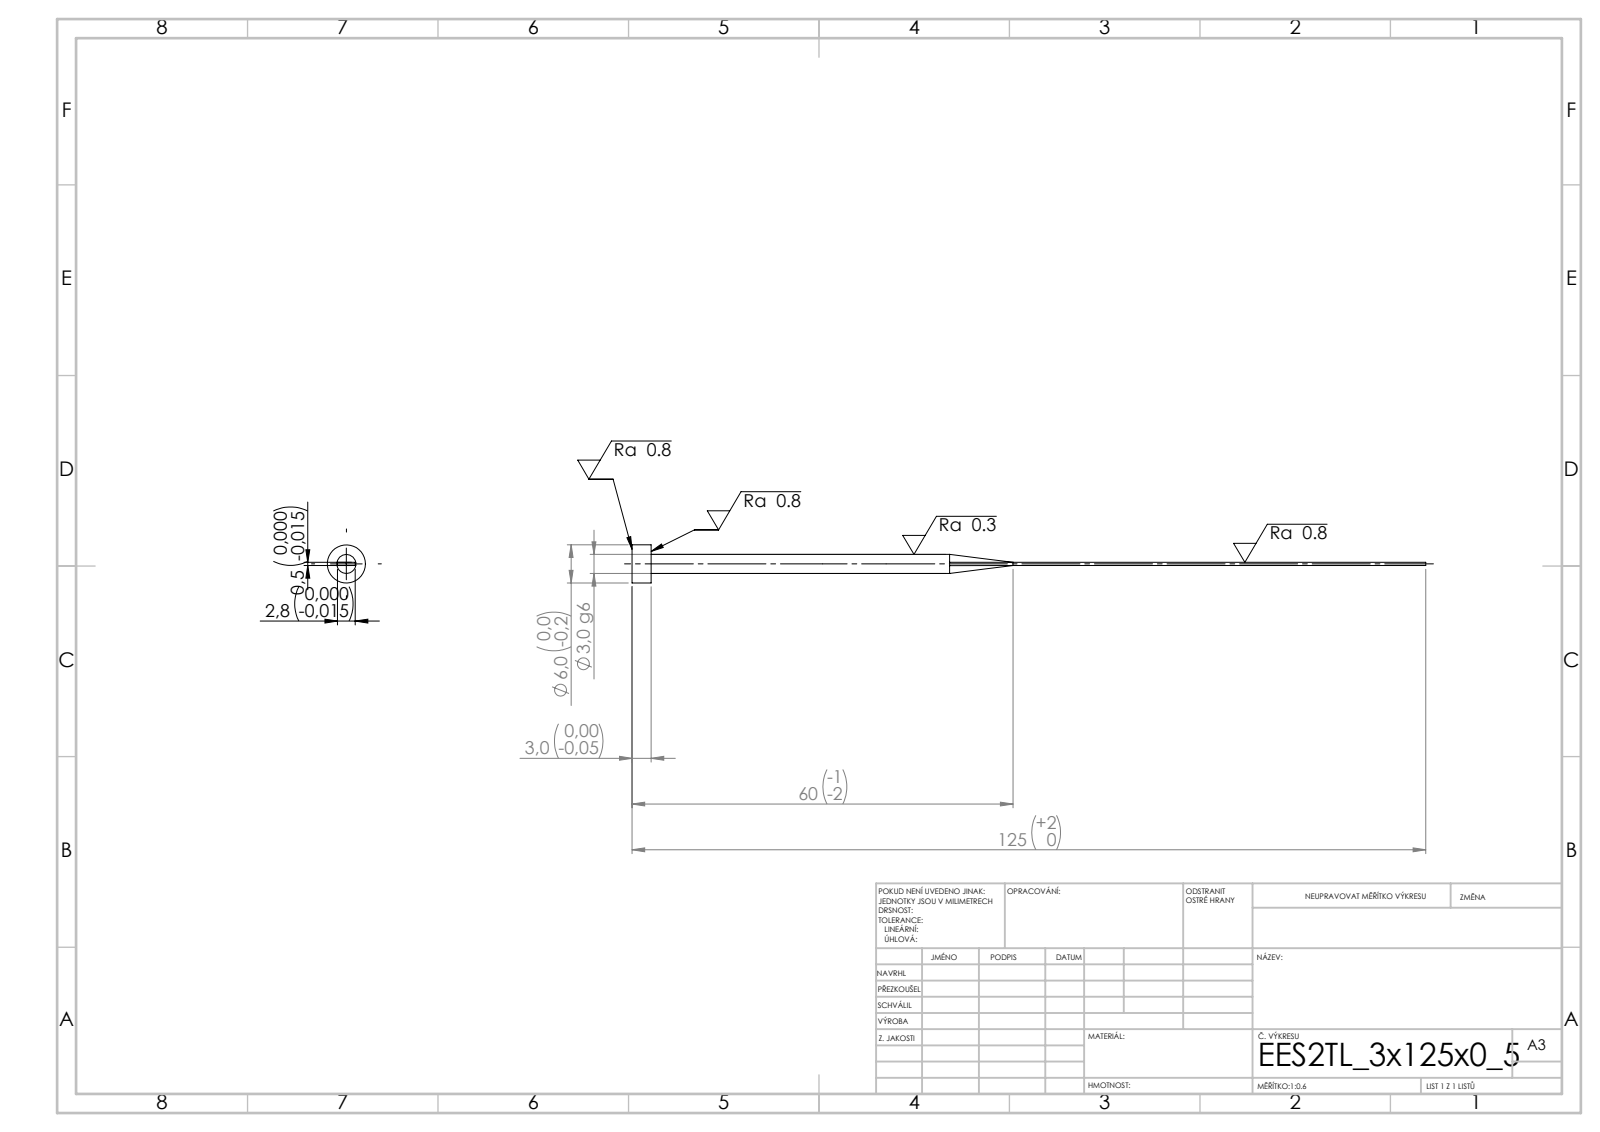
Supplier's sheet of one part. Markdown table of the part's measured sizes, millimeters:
| quantity | value |
| --- | --- |
| STEP written by | SolidWorks 2019 (CONFIG_CONTROL_DESIGN) |
| units | millimeters |
| bodies | 1 solid, 15 faces (7 planar, 4 cylindrical, 4 other) |
| overall size | 125 × 6 × 6 |
| volume | 548 mm³ |
| surface area | 1 056 mm² |
| round bosses / shafts (diameter × count) | 6 × 1, 3 × 1 |
| main face-to-face distances | 0.5, 2.8, 3, 125, 122 |
